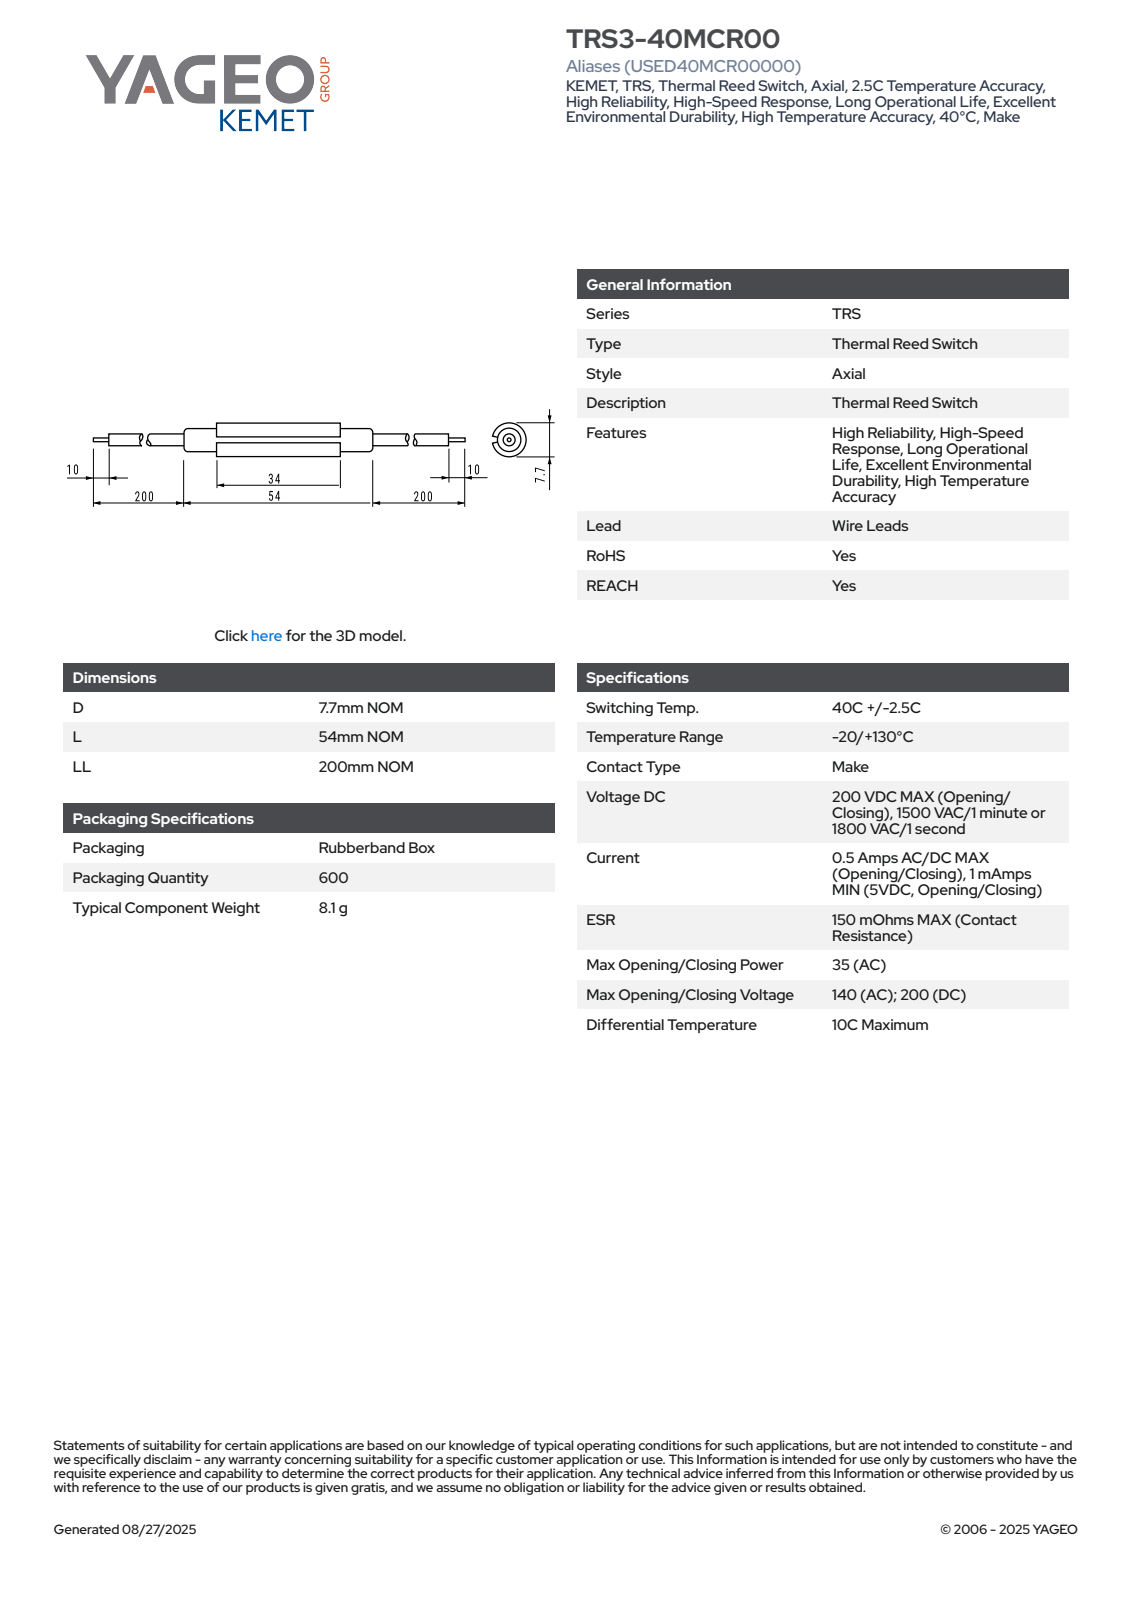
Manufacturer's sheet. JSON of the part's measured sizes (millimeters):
{"part_name": "ST_TRSMC0_D7.7L54LL200", "step_written_by": "SolidWorks 2014 (AUTOMOTIVE_DESIGN)", "units": "millimeters", "bodies": {"solids": 1, "faces": 86, "planar": 32, "cylindrical": 15, "other": 39}, "overall_size": [454, 7.7, 7.63], "volume_mm3": 4390, "surface_area_mm2": 4683, "round_bosses_or_shafts": [[7.7, 1], [5.7, 1], [2.8, 1], [0.5, 1]], "partial_cylinders_radius": [[3.84, 1]], "face_to_face_distances": [10, 44, 200, 244, 190, 234, 54, 34, 434, 210]}
